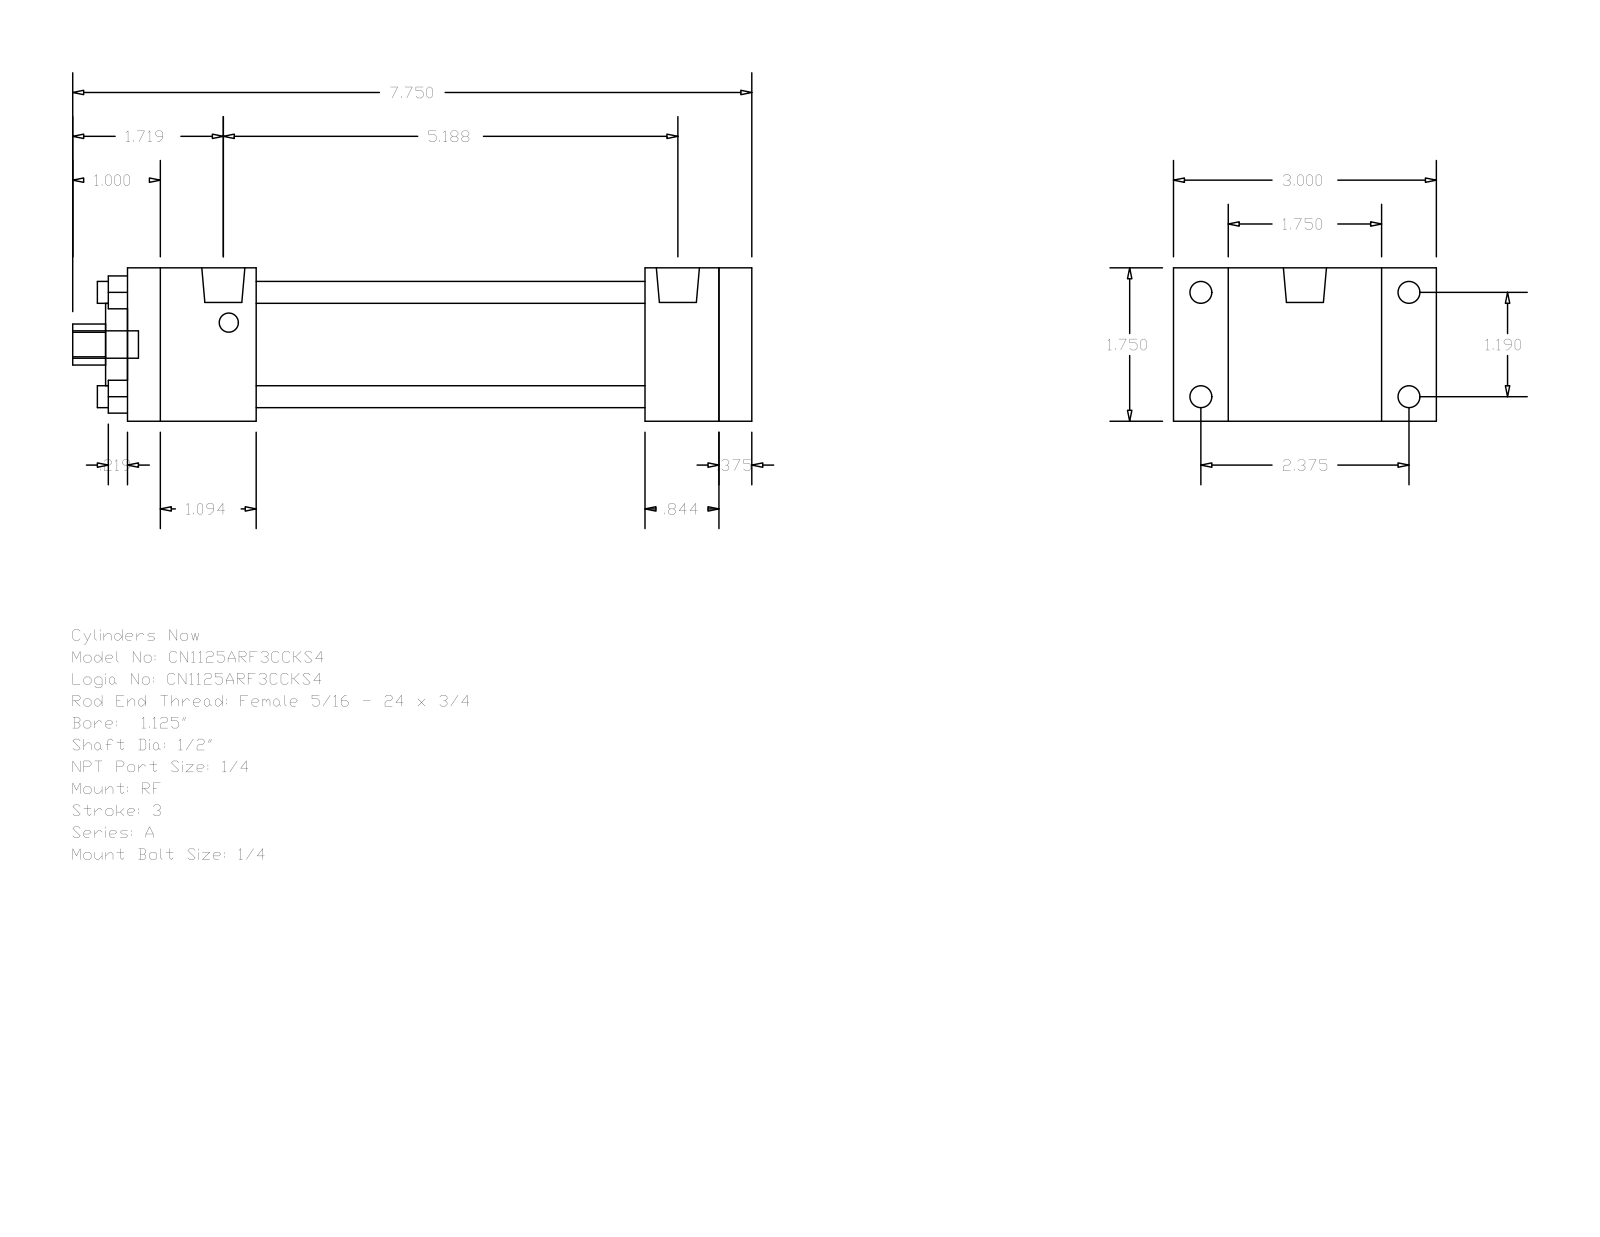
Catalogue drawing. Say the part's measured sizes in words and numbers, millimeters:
The part is named "A_RF__0112_0.5". Its 3-D file was written by "GSSL Pune (CONFIG_CONTROL_DESIGN)". It is 0 solids with 92 faces: 64 planar, 28 cylindrical and 0 other. Overall it measures 196.85 by 76.2 by 44.45 millimeters. Round holes: 4 of diameter 6.35, 1 of diameter 12.7, 1 of diameter 23.81, 1 of diameter 31.88. Round bosses or shafts: 4 of diameter 6.35, 4 of diameter 5.56, 2 of diameter 12.49, 1 of diameter 7.94. Partial cylindrical surfaces (rounded edges, fillets, slot ends): 1 of radius 5.94. The main face-to-face distances are 44.46, 9.53, 180.97, 171.44, 37.3, 150.01, 112.71, 134.14, 143.67, 21.43. The hole center spacings are 21.37, 30.22, 42.74.
